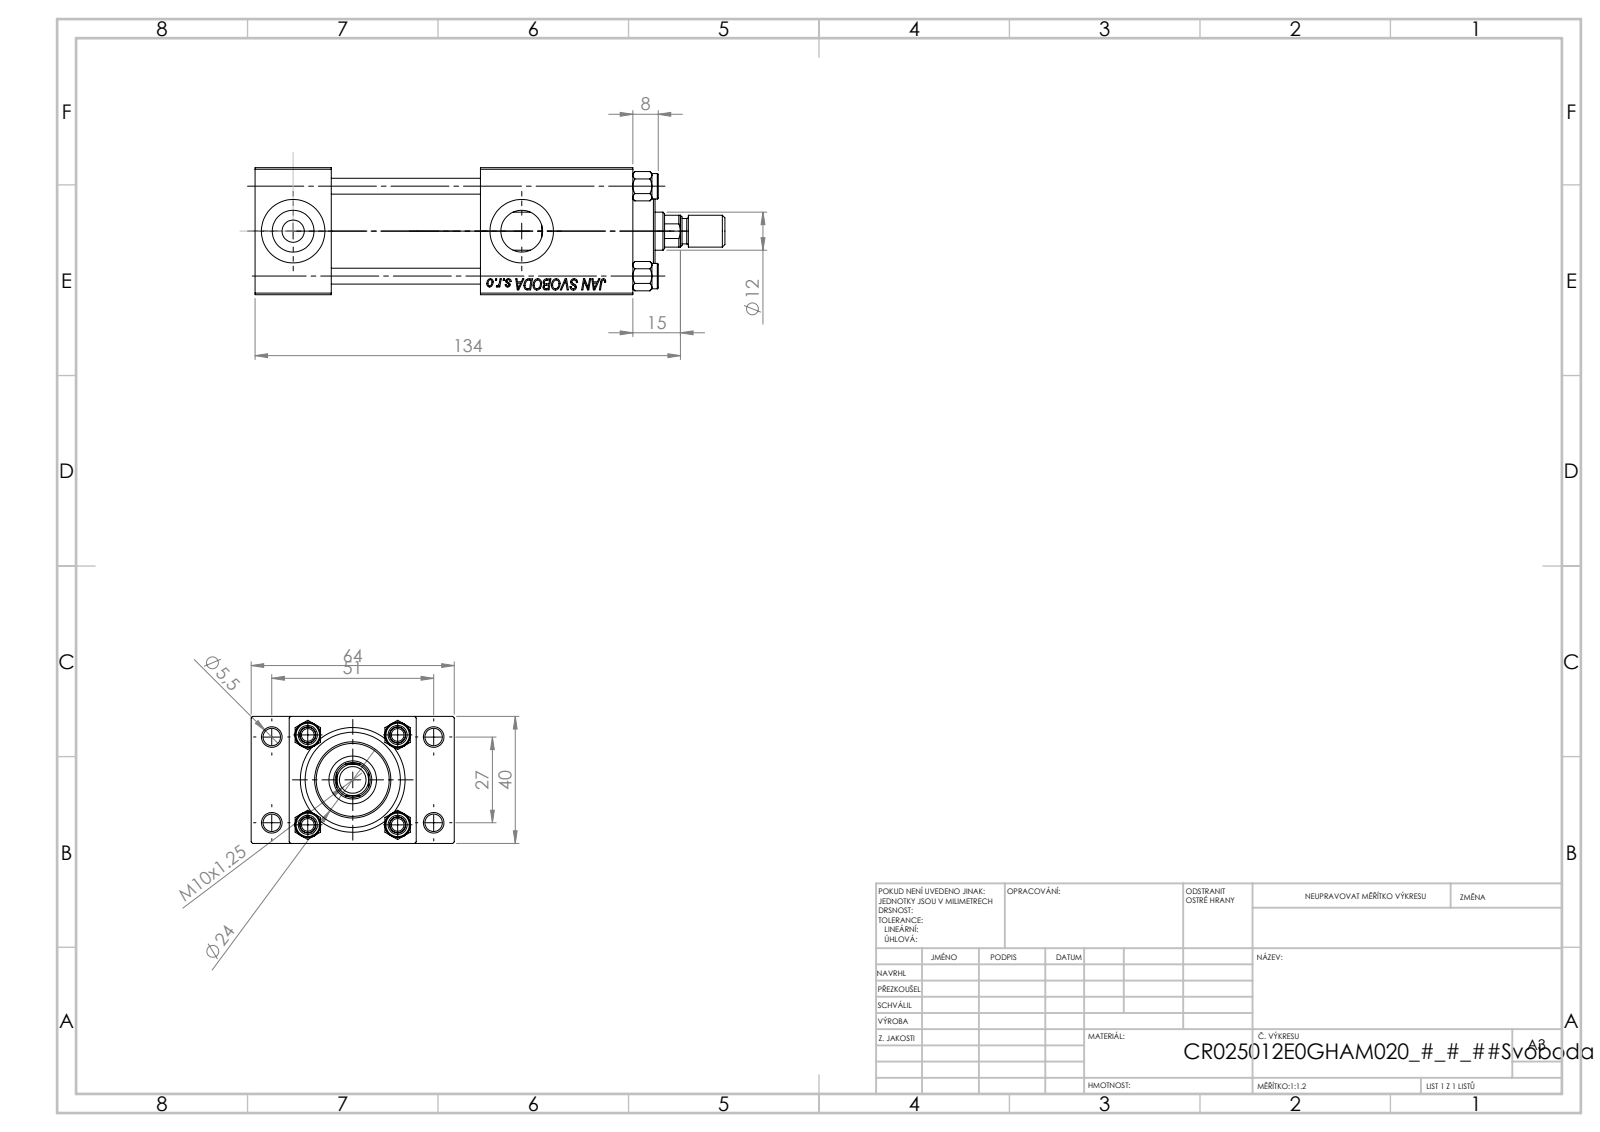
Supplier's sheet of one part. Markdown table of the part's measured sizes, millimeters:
| quantity | value |
| --- | --- |
| part name | V215CR_TYCINKA_E; V215_VC_A; V215CR_E_Body; V215CR_VCP_E (+2 more) |
| STEP written by | SolidWorks 2019 (CONFIG_CONTROL_DESIGN) |
| units | millimeters |
| bodies | 12 solids, 1149 faces (501 planar, 90 cylindrical, 558 other) |
| overall size | 148 × 64 × 40 |
| volume | 164 565 mm³ |
| surface area | 62 978 mm² |
| round holes (diameter × count) | 5 × 4, 5.5 × 4, 20 × 3, 7 × 2, 13.16 × 2, 6.5 × 1, 12 × 1, 15 × 1, 25 × 1, 30 × 1 |
| round bosses / shafts (diameter × count) | 8 × 5, 31 × 1, 24 × 1, 10 × 1 |
| partial cylindrical surfaces (radius × count) | 5.5 × 1 |
| main face-to-face distances | 40, 24, 12, 52, 119, 95, 90.3, 66.3, 28.7, 47 |
| hole center spacings | 11.37, 20.01, 28.3, 28.85, 29.89, 39.66, 48.34, 27 |
